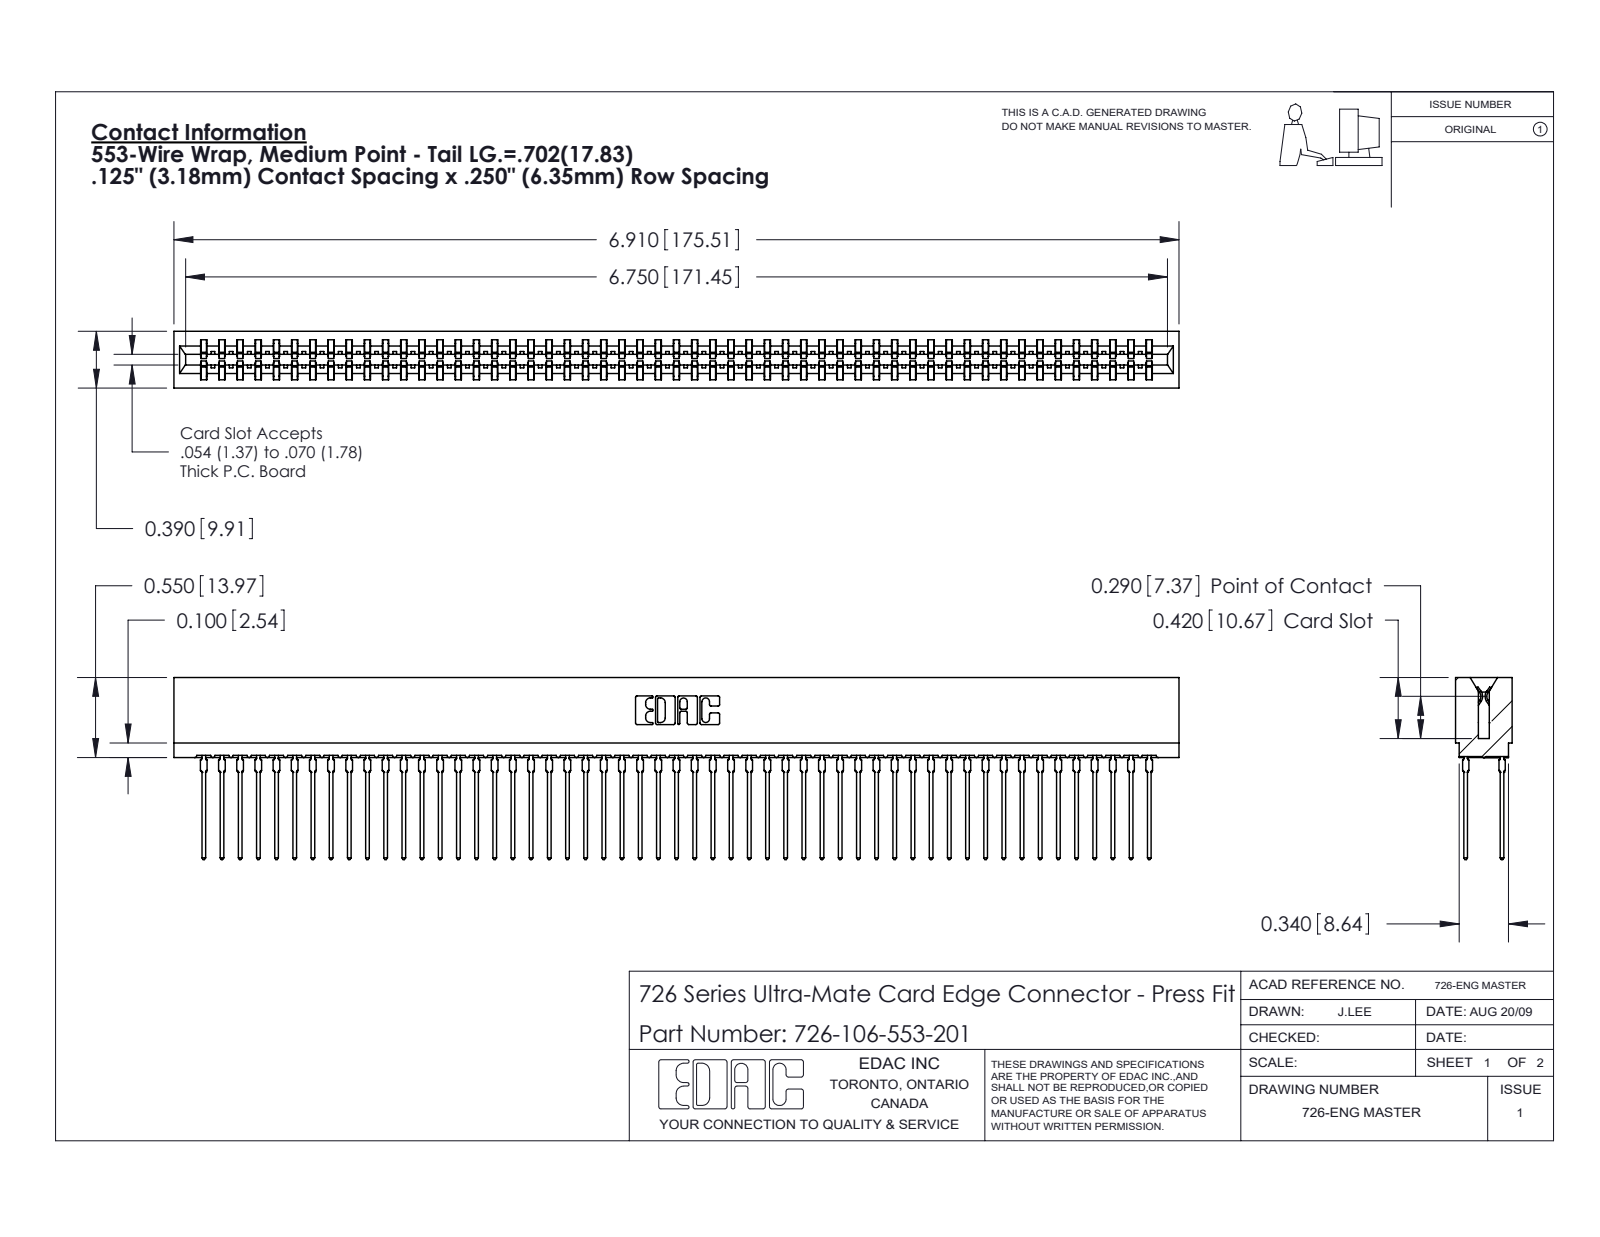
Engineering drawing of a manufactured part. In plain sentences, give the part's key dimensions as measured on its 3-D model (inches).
The part is named "726 Part_.515 Slot Depth - 01; 746-292-001_553; 726-106-553-201". Its 3-D file was written by "SolidWorks 2020 (CONFIG_CONTROL_DESIGN)". It is 107 solids with 9584 faces: 4931 planar, 1897 cylindrical and 2756 other. Overall it measures 6.91 by 1.251 by 0.39 inches. Its volume is 1.011 cubic inches and its surface area 46.42 square inches. Partial cylindrical surfaces (rounded edges, fillets, slot ends): 212 of radius 0.021, 54 of radius 0.015, 22 of radius 0.01, 8 of radius 0.005, 8 of radius 0.011, 6 of radius 0.007, 6 of radius 0.031, 3 of radius 0.026. The main face-to-face distances are 0.057, 0.333, 0.025, 0.307, 0.25, 0.39, 0.083, 0.275, 0.225, 0.365.
